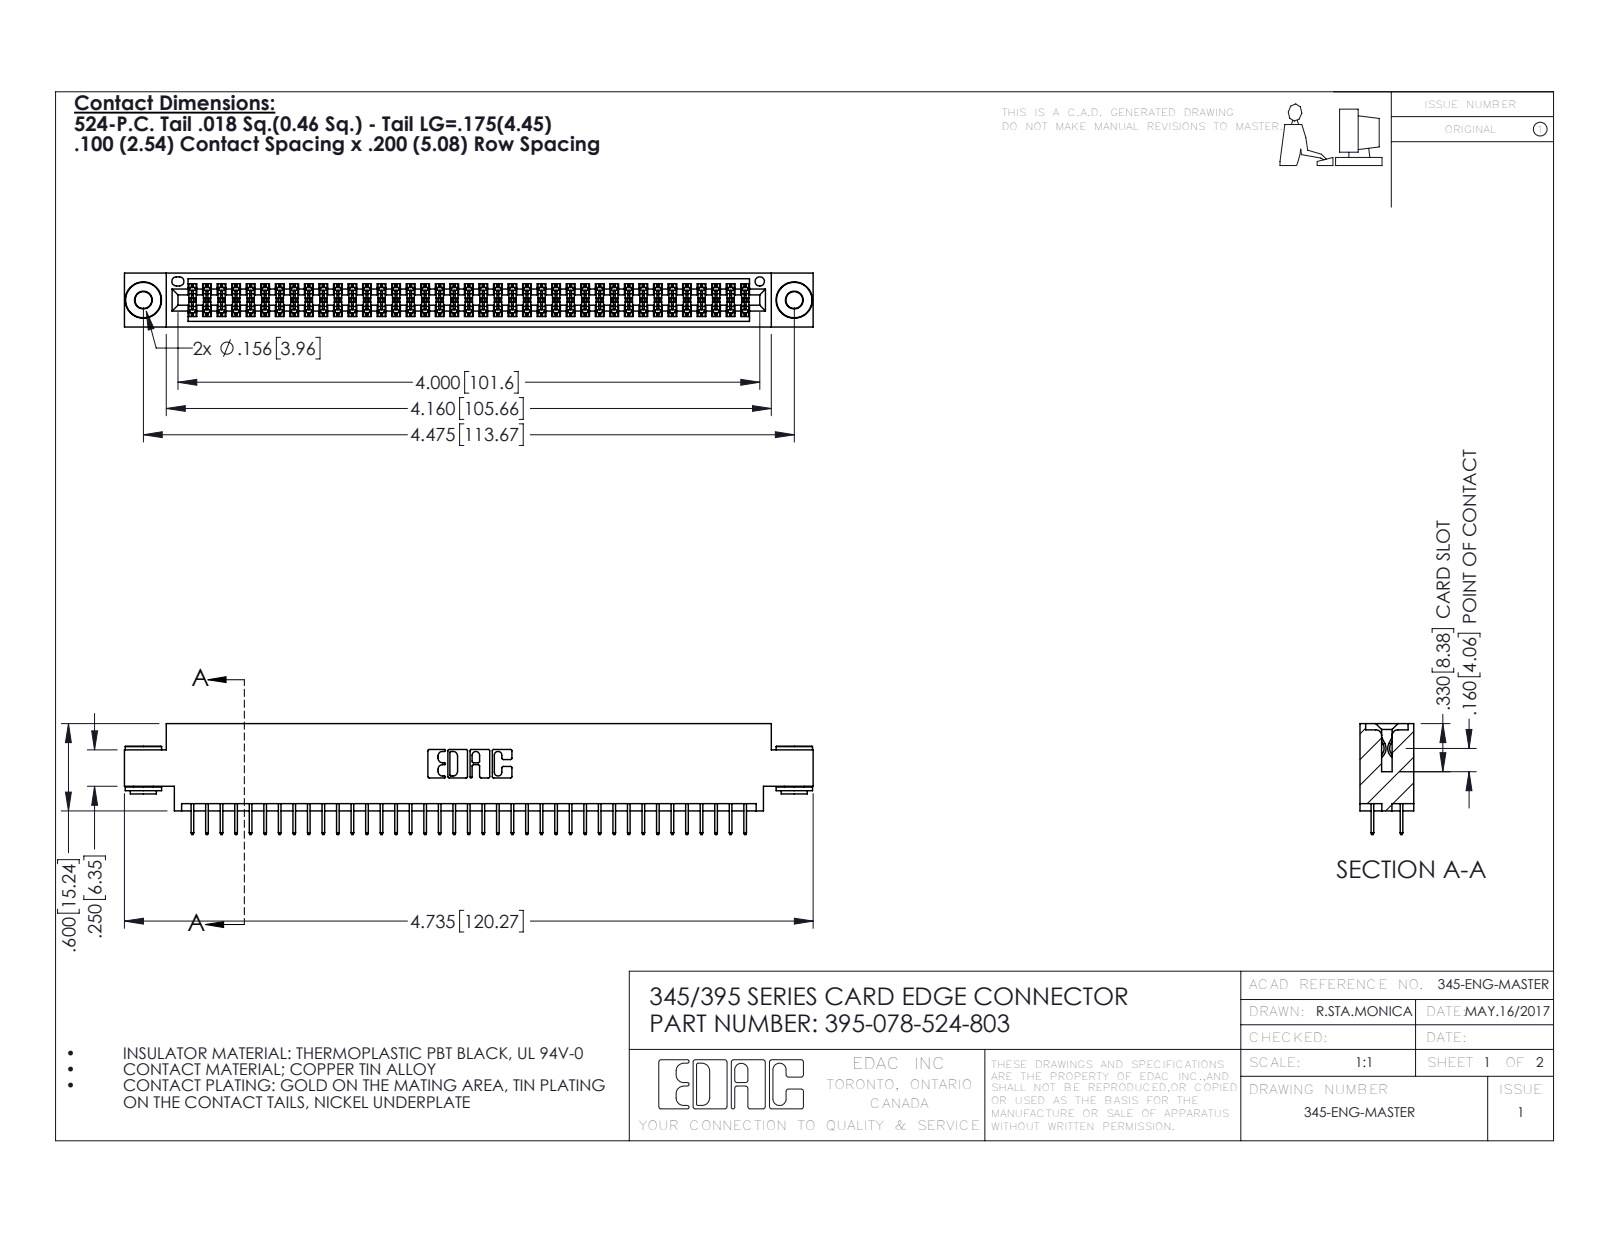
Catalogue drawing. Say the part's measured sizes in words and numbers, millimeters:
The part is named "345 Part_0.170 Offset - 0.156 Dia-TH; 395-078-524-803; 345-292-001_345-293-124; 345-250-002_345-250-002-102". Its 3-D file was written by "SolidWorks 2016 (CONFIG_CONTROL_DESIGN)". It is 81 solids with 4380 faces: 3136 planar, 1236 cylindrical and 8 other. Overall it measures 120.3 by 19.4 by 9.4 millimeters. Its volume is 11 400 cubic millimeters and its surface area 16 900 square millimeters. Round holes: 2 of diameter 2.9, 2 of diameter 4, 1 of diameter 1.6. Round bosses or shafts: 2 of diameter 6.4, 2 of diameter 4.6, 2 of diameter 3.5. Partial cylindrical surfaces (rounded edges, fillets, slot ends): 117 of radius 0.2, 22 of radius 0.3, 6 of radius 0.2, 6 of radius 0.8, 3 of radius 0.7, 2 of radius 0.4, 2 of radius 0.5, 2 of radius 0.6. The main face-to-face distances are 1.8, 7.6, 9.4, 5.1, 2.5, 6.9, 0.6, 5.7, 4.4, 1.8. The hole center spacings are 6.9, 107.7, 113.7.
